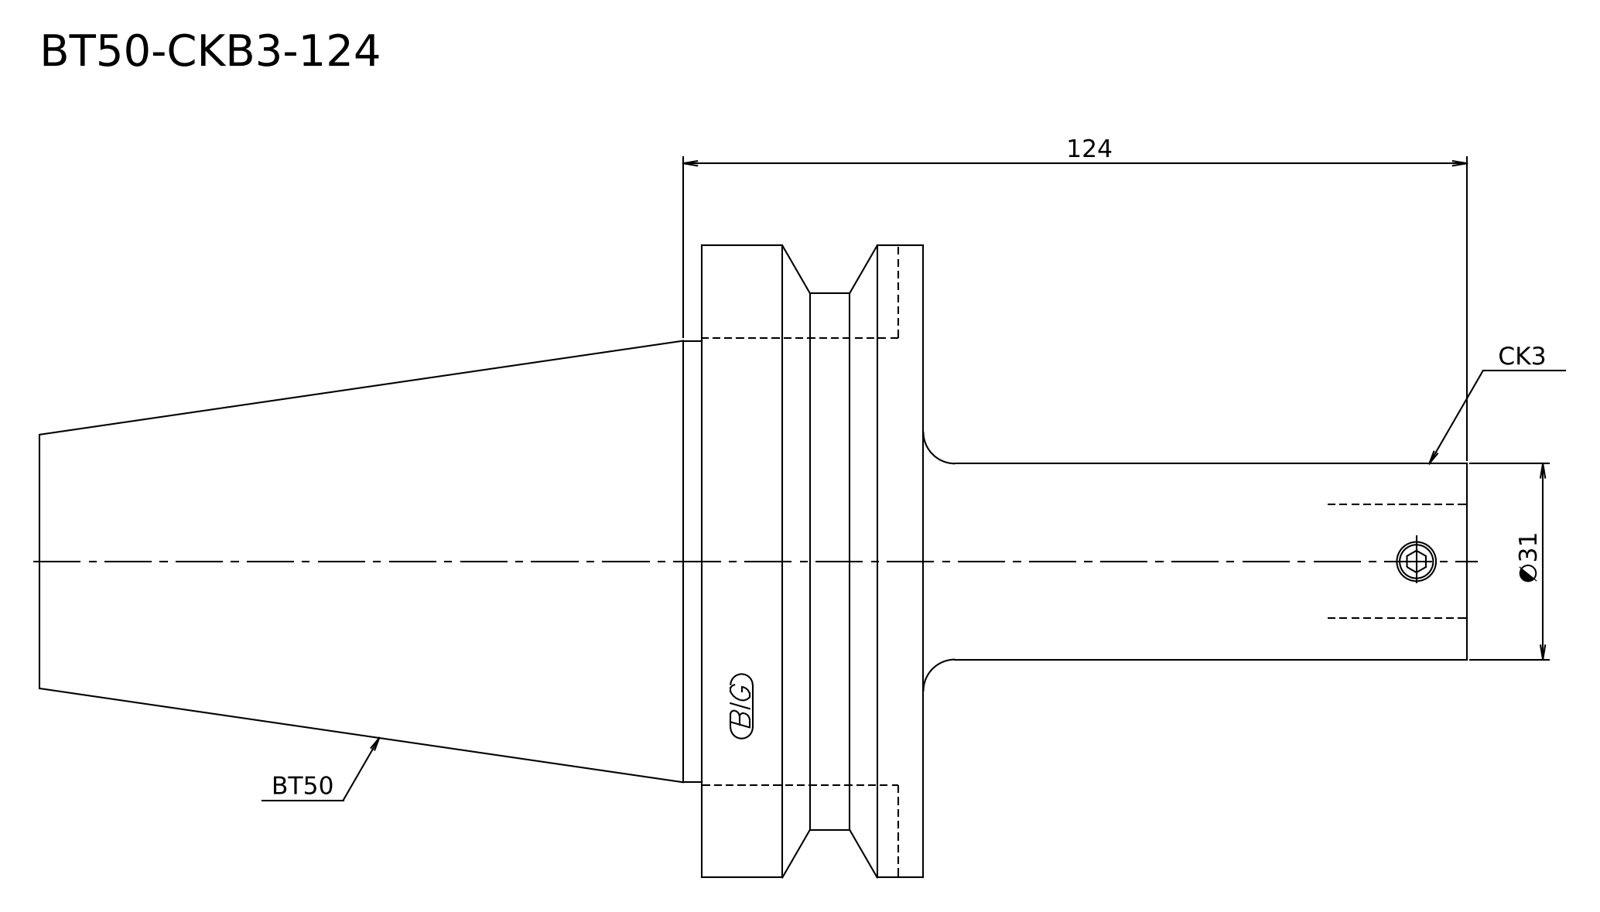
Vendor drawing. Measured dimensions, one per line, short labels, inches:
written by: Kubotek KeyCreator V8.5.1 (14335) (CONFIG_CONTROL_DESIGN)
unit: in
bodies: 1 solid, 13 faces (4 planar, 5 cylindrical, 4 other)
size: 8.89 × 3.937 × 3.937
volume: 35.2 in³; area: 81.7 in²
bosses: 1× ⌀3.937, 1× ⌀3.346, 1× ⌀2.75, 1× ⌀1.22
face distances: 1.378, 5.504, 4.126, 3.386, 4.764, 8.89
